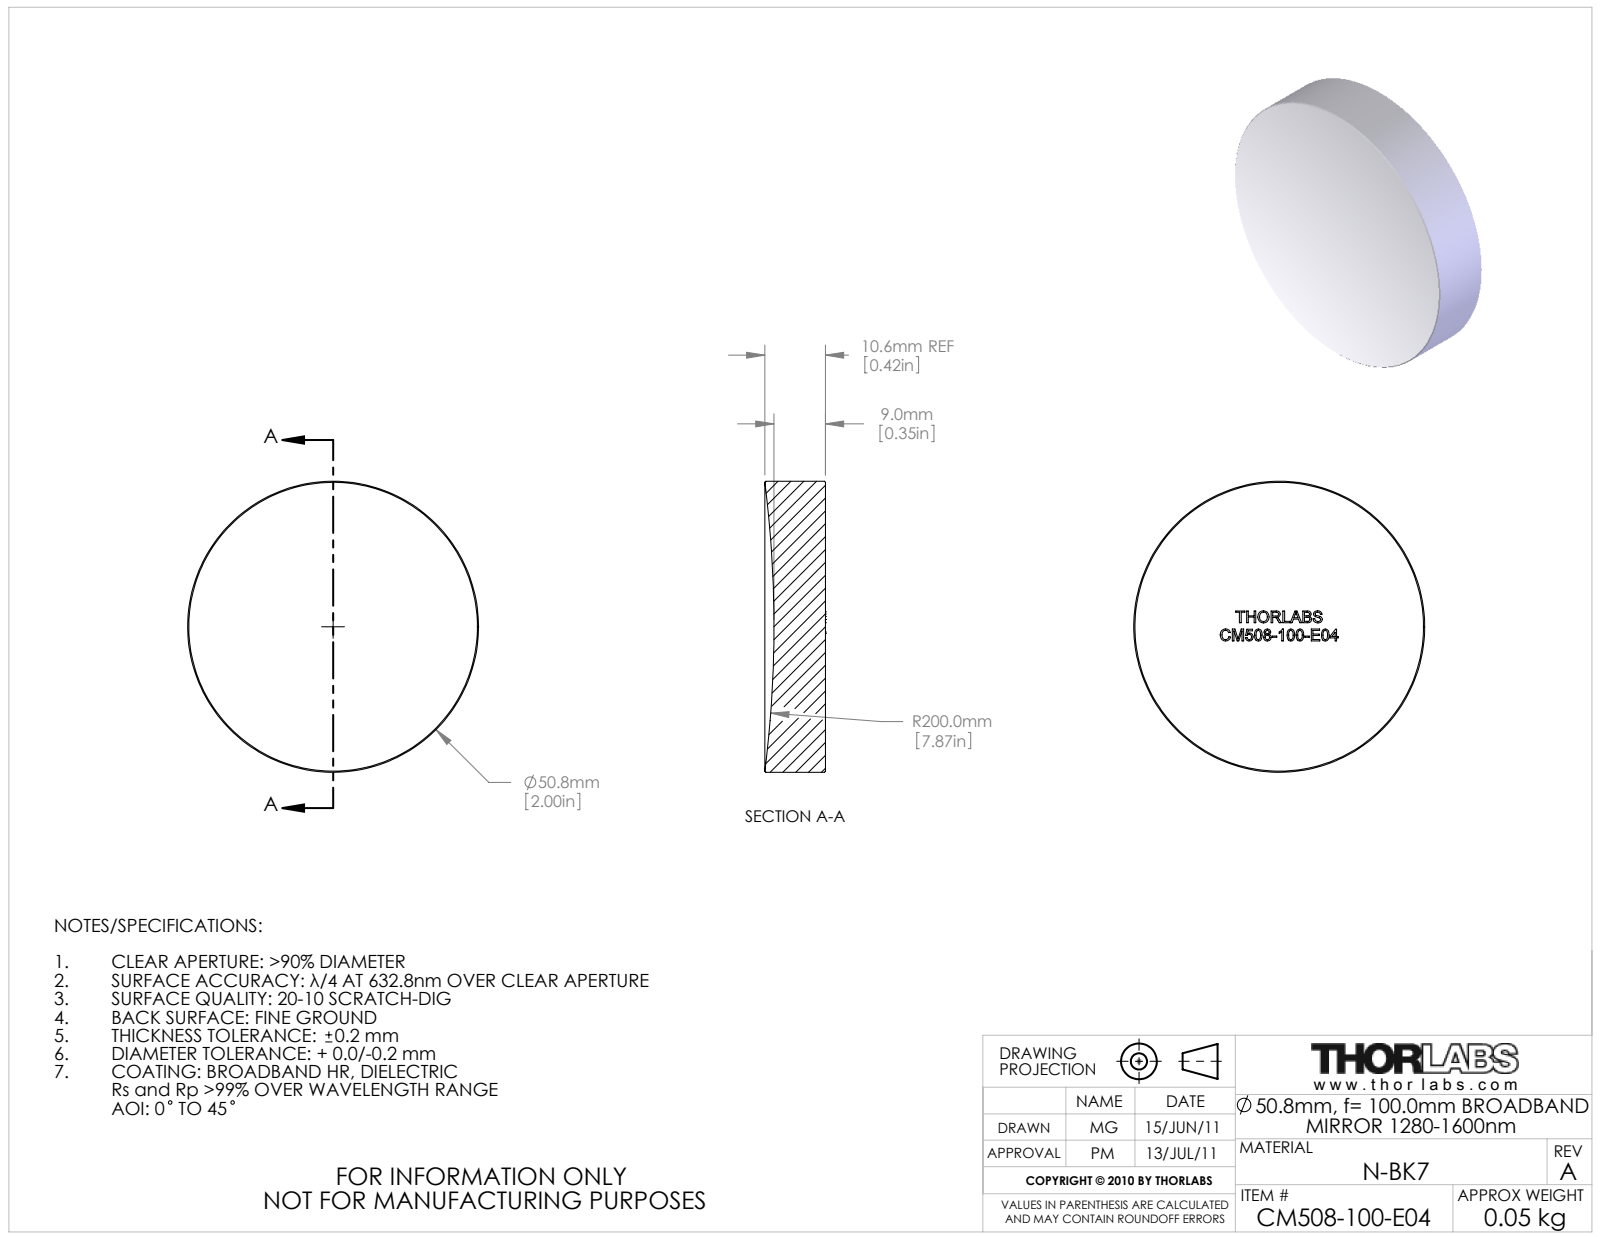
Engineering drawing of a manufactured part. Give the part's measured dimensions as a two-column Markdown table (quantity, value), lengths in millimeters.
| quantity | value |
| --- | --- |
| part name | 22661-E0W |
| STEP written by | SolidWorks 2011 (AUTOMOTIVE_DESIGN) |
| units | millimeters |
| bodies | 0 solids, 43 faces (35 planar, 2 cylindrical, 6 other) |
| overall size | 50.8 × 50.8 × 10.59 |
| round bosses / shafts (diameter × count) | 50.8 × 1 |
